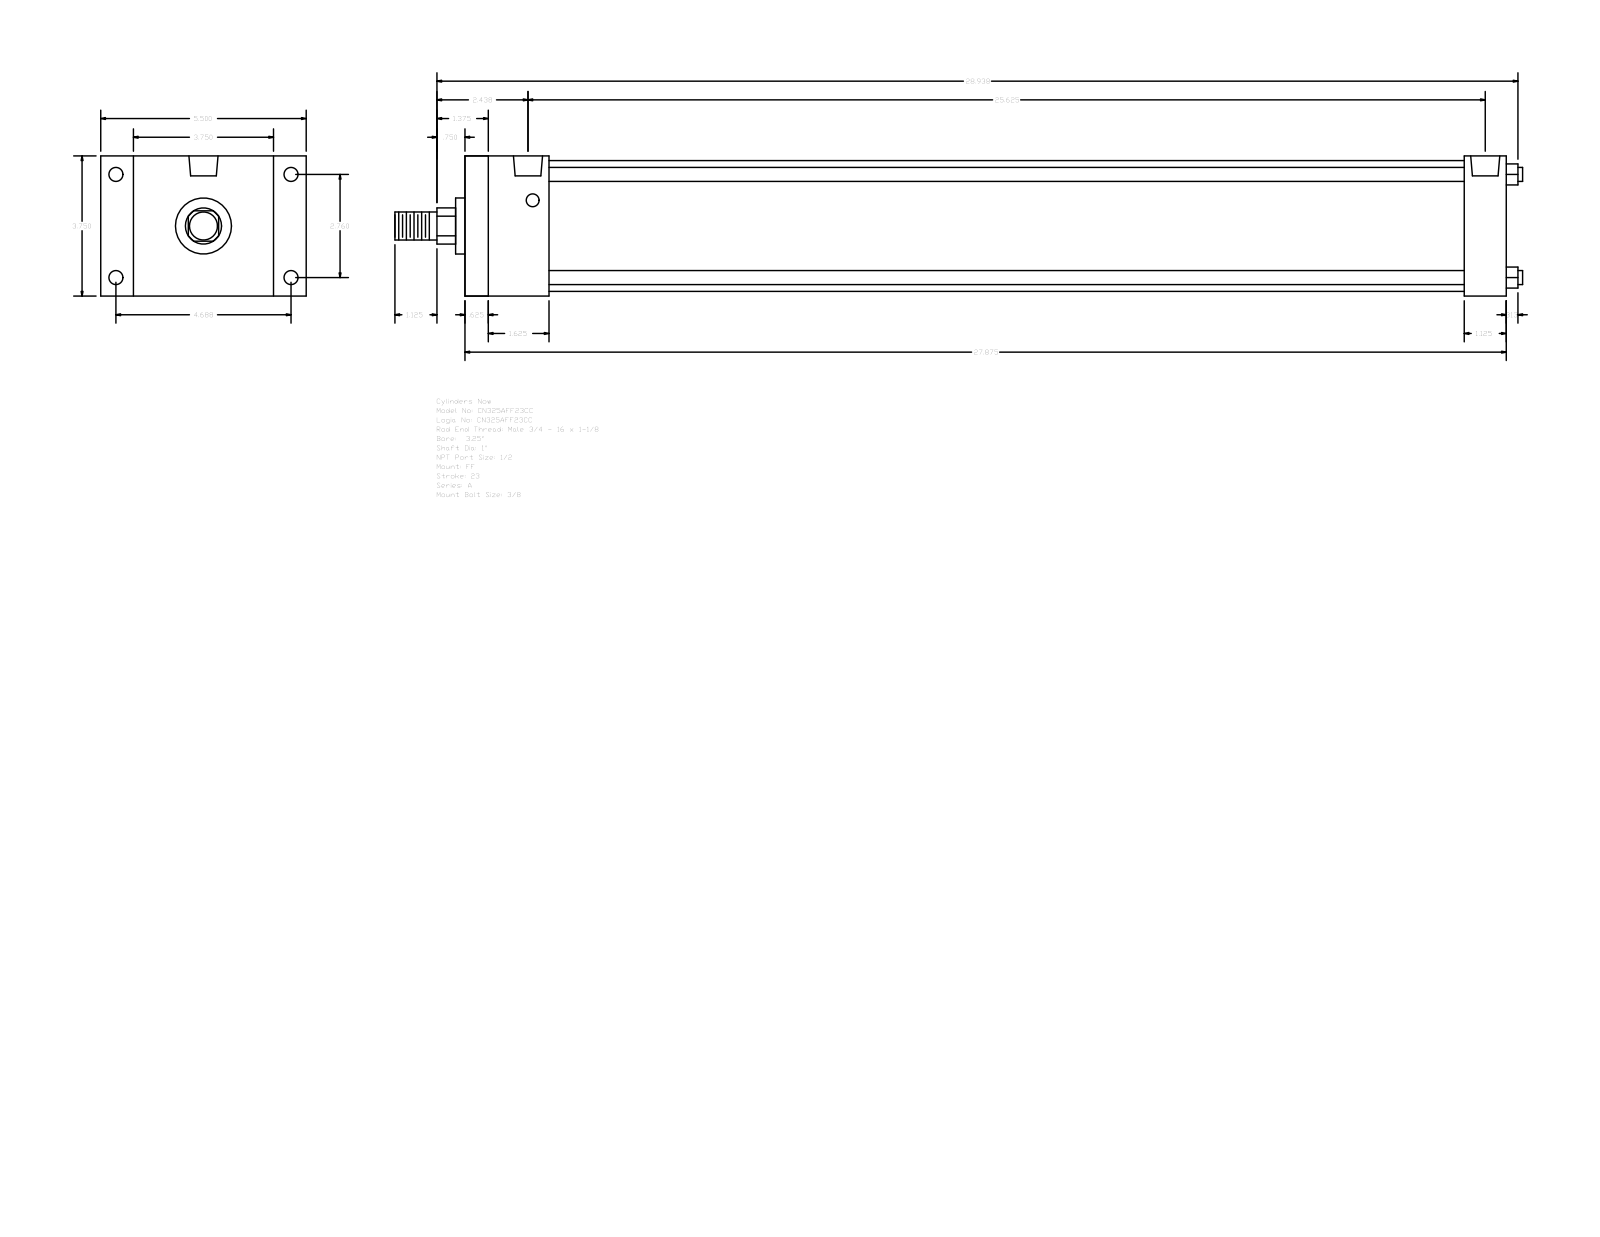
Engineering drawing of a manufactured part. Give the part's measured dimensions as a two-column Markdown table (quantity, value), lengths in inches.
| quantity | value |
| --- | --- |
| part name | A_FF__0325_1 |
| STEP written by | GSSL Pune (CONFIG_CONTROL_DESIGN) |
| units | inches |
| bodies | 0 solids, 92 faces (64 planar, 28 cylindrical, 0 other) |
| overall size | 30.187 × 5.5 × 3.75 |
| round holes (diameter × count) | 0.344 × 4, 0.375 × 4, 0.778 × 2 |
| round bosses / shafts (diameter × count) | 0.375 × 4, 3.5 × 1, 1.5 × 1, 1 × 1, 0.75 × 1 |
| partial cylindrical surfaces (radius × count) | 0.484 × 1 |
| main face-to-face distances | 3.75, 27.875, 0.625, 27.25, 0.875, 4.625, 2.25, 26.75, 1.625, 26.125 |
| hole center spacings | 0.125, 2.76, 4.687, 5.439, 25.375, 25.5, 25.625 |
